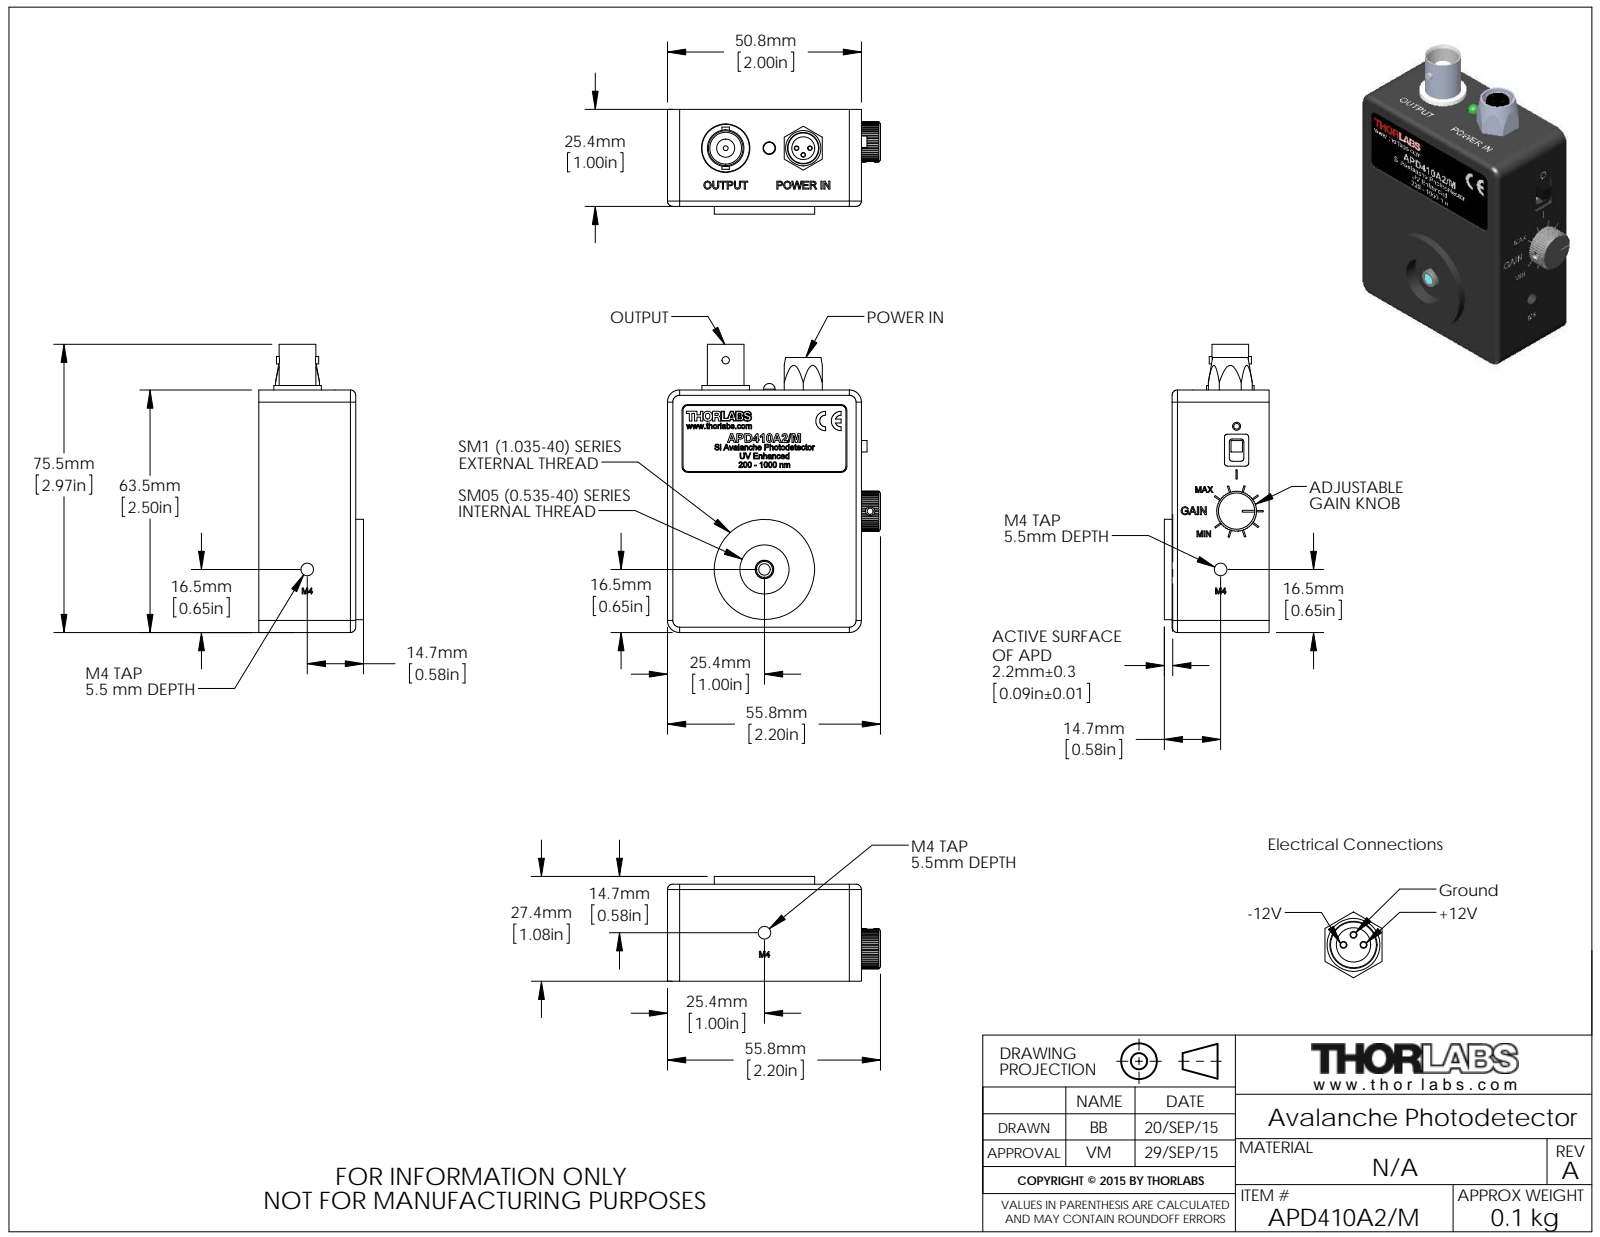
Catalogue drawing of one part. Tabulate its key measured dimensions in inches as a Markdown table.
| quantity | value |
| --- | --- |
| part name | MTN005413 |
| STEP written by | SolidWorks 2014 (AUTOMOTIVE_DESIGN) |
| units | inches |
| bodies | 0 solids, 2464 faces (1338 planar, 436 cylindrical, 690 other) |
| overall size | 2.971 × 2.197 × 1.08 |
| round holes (diameter × count) | 0.063 × 9, 0.02 × 6, 0.094 × 4, 0.018 × 2, 0.098 × 2, 0.13 × 2, 0.05 × 1, 0.052 × 1, 0.083 × 1, 0.118 × 1, 0.13 × 1, 0.138 × 1 |
| round bosses / shafts (diameter × count) | 0.039 × 5, 0.15 × 4, 0.079 × 4, 0.065 × 2, 0.063 × 2, 0.051 × 2, 1.035 × 1, 0.49 × 1 |
| partial cylindrical surfaces (radius × count) | 0.012 × 53, 0.125 × 19, 0.13 × 14, 0.031 × 8, 0.095 × 8, 0.02 × 6, 0.075 × 6, 0.008 × 5 |
| main face-to-face distances | 0.063, 0.1, 0.016, 0.935, 0.872, 0.065, 1, 0.937, 0.984, 0.922 |
| hole center spacings | 1.621, 0.174, 2.013, 2.579, 0.098, 1.711, 0.05, 0.079 |
